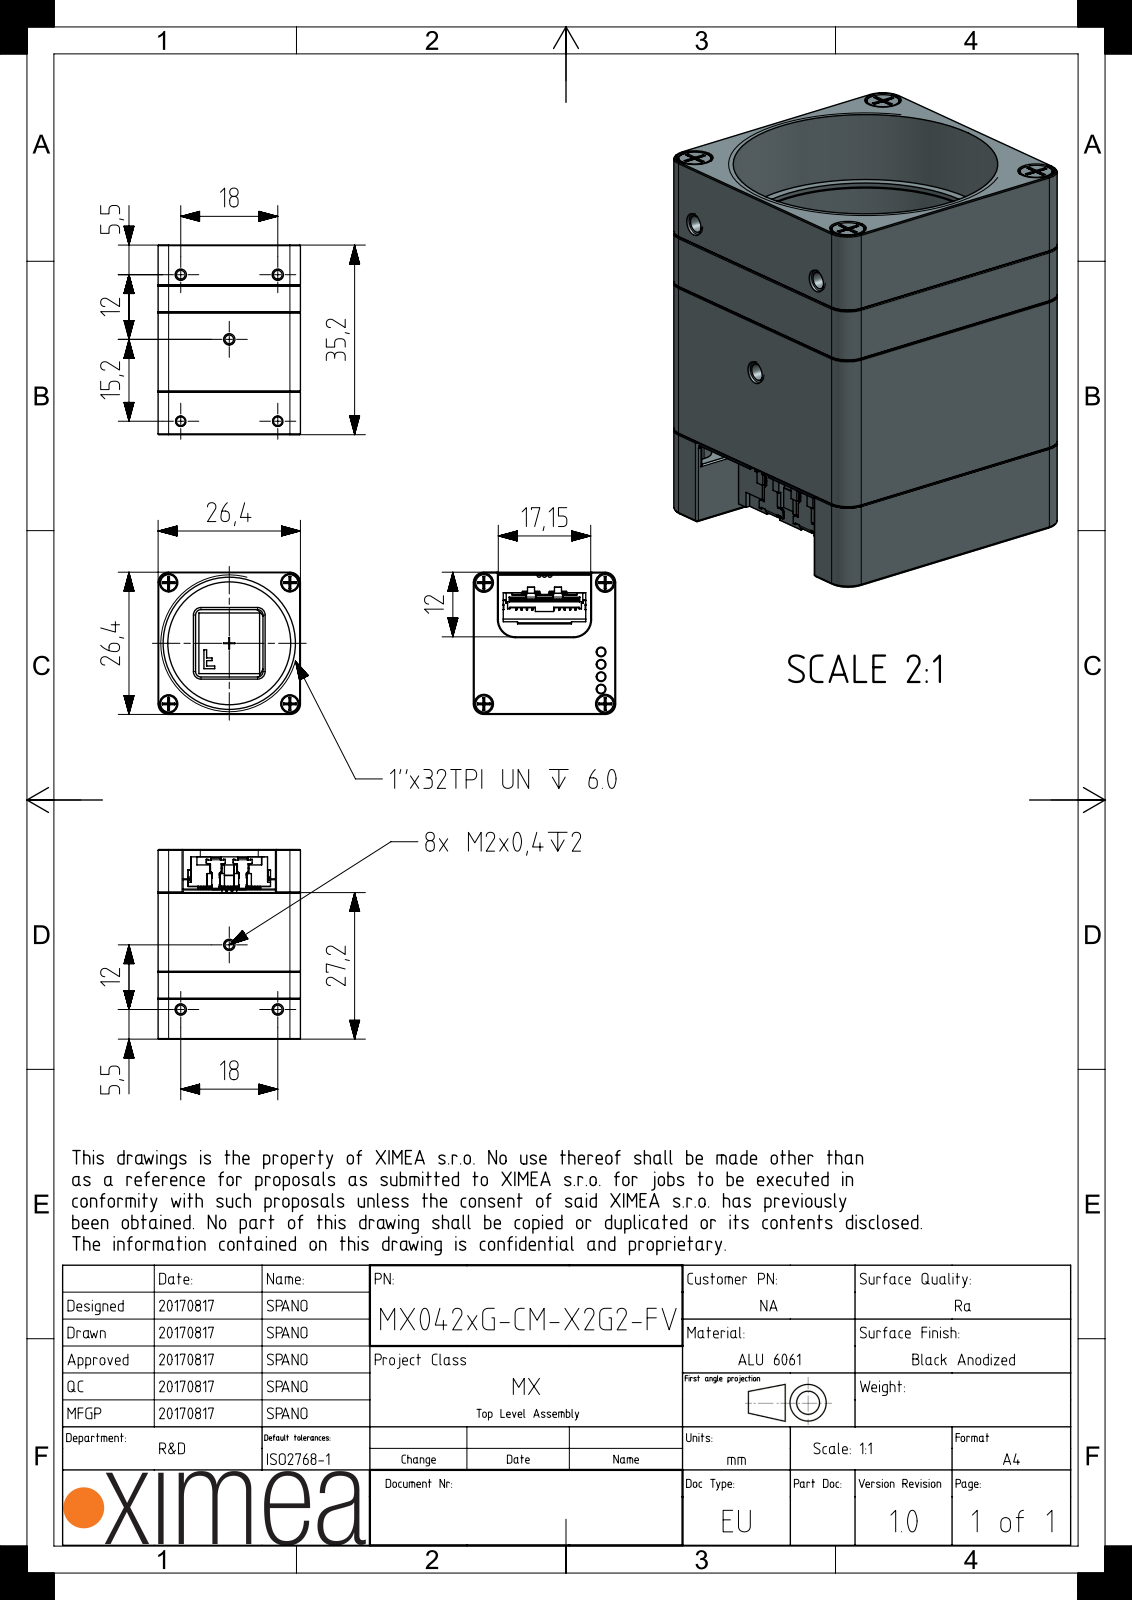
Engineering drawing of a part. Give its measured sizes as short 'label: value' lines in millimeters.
name: CMV4000_Glass; CMV4000_Package; ANDON-96UPGA-Socket; SROB-M2x10-CUST (+8 more)
written by: SIEMENS PLM Software NX 1907 (AUTOMOTIVE_DESIGN)
unit: mm
bodies: 405 solids, 12043 faces (7288 planar, 3461 cylindrical, 1294 other)
size: 35.2 × 26.4 × 26.4
volume: 12 100 mm³; area: 23 550 mm²
holes: 95× ⌀0.5, 95× ⌀0.8, 13× ⌀1.6, 4× ⌀0.9, 4× ⌀1.8, 4× ⌀2, 4× ⌀2.1, 4× ⌀3, 4× ⌀3.2, 4× ⌀3.4, 1× ⌀1.4, 1× ⌀1.9
bosses: 95× ⌀0.3, 4× ⌀1.9, 4× ⌀1.6, 4× ⌀0.8, 2× ⌀3, 2× ⌀1.6, 1× ⌀25, 1× ⌀21.6
rounds: 82× R0.2, 32× R0.1, 20× R1, 18× R0.4, 17× R1.5, 16× R0.3, 16× R1.3, 9× R0.2
face distances: 1, 26.4, 3.6, 11.1, 4.6, 8.1, 4.5, 15.8, 11.2, 14.8
hole spacings: 2.8, 6.4, 4, 6.8, 4.6, 5.2, 9, 5.4
